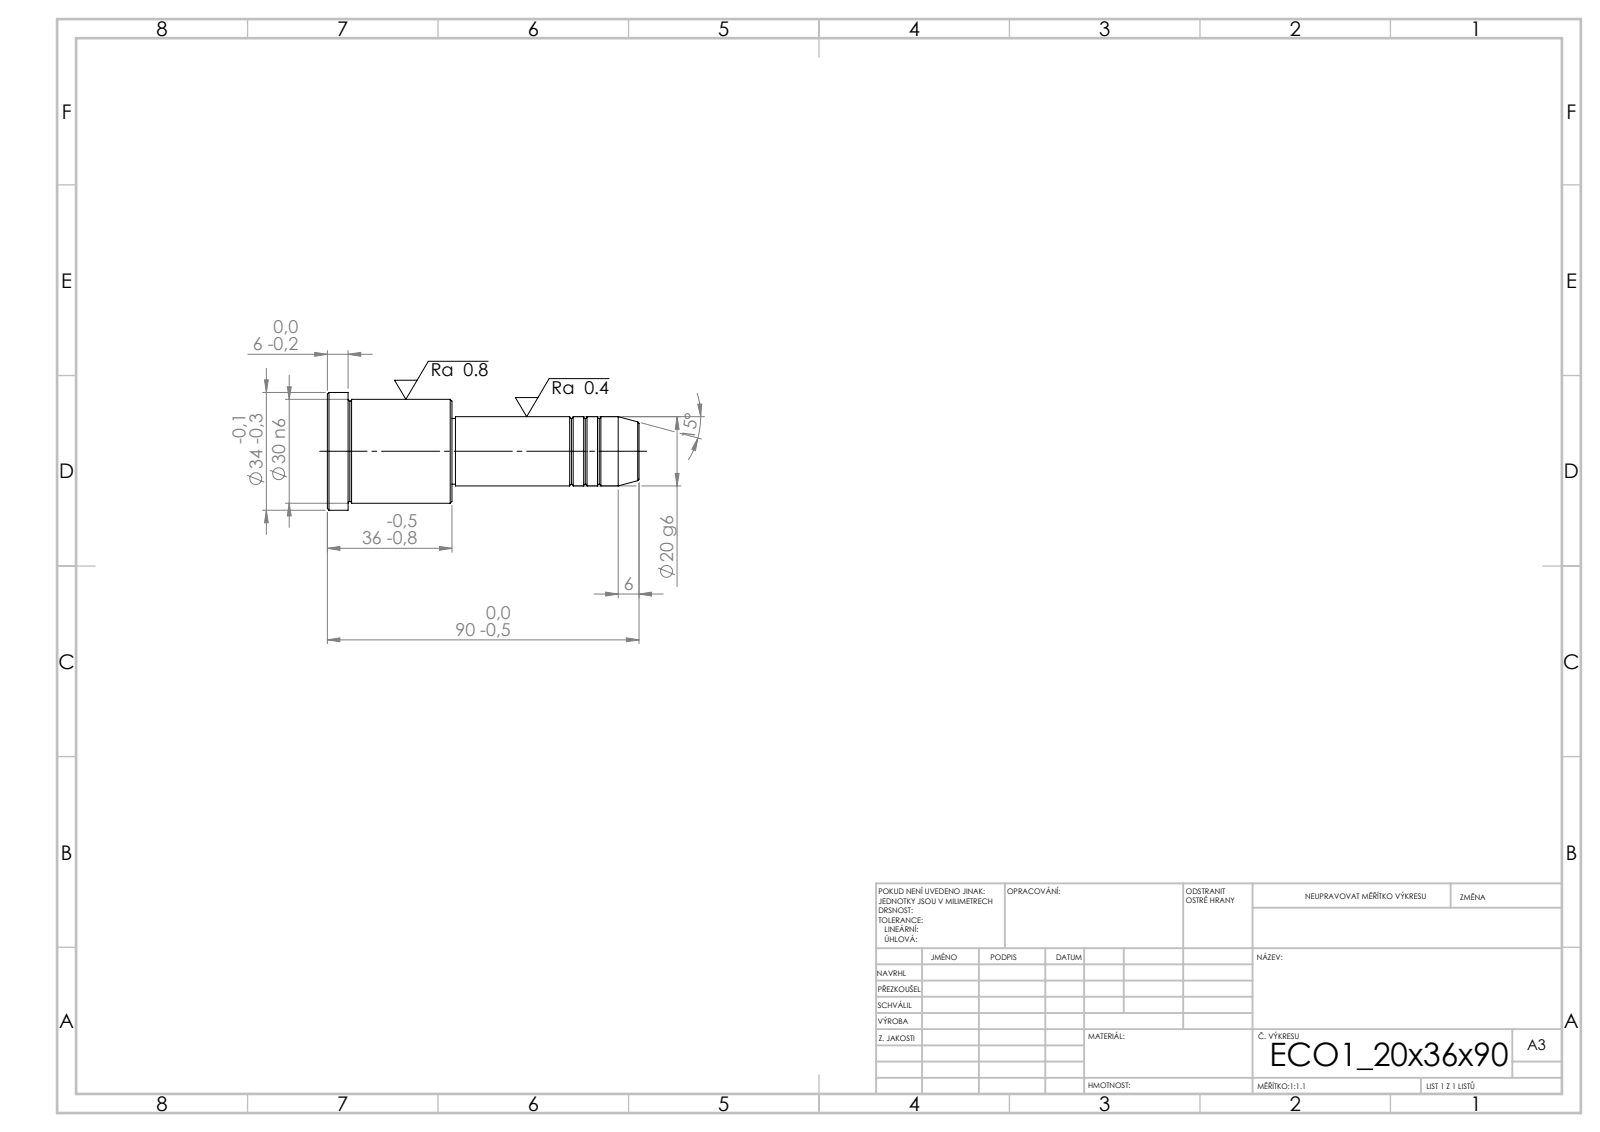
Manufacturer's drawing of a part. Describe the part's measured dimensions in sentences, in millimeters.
Its 3-D file was written by "SolidWorks 2019 (CONFIG_CONTROL_DESIGN)". It is 1 solid with 43 faces: 5 planar, 14 cylindrical and 24 other. Overall it measures 90 by 34 by 34 millimeters. Its volume is 43 165 cubic millimeters and its surface area 8 707 square millimeters. Round bosses or shafts: 1 of diameter 34, 1 of diameter 30, 1 of diameter 20, 1 of diameter 19. The main face-to-face distances are 36, 54, 90, 84, 30, 6, 53, 1, 31, 37.
